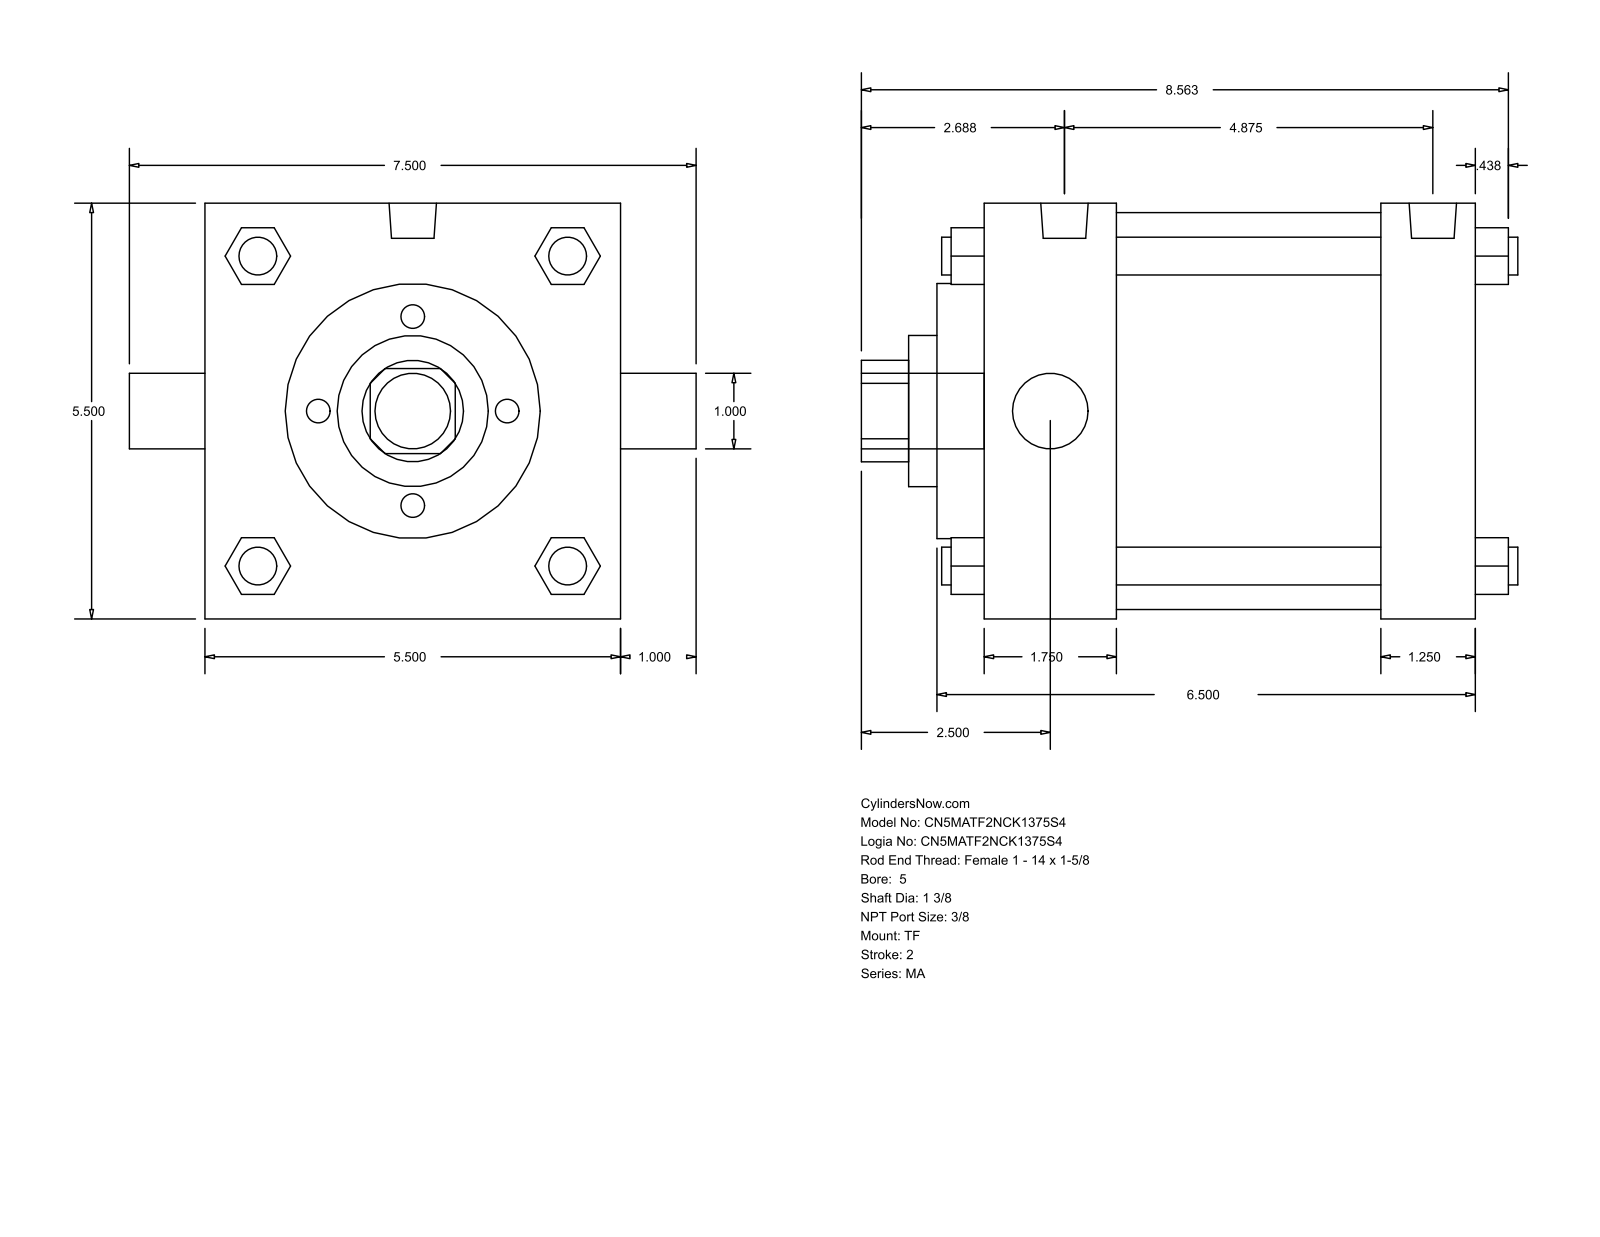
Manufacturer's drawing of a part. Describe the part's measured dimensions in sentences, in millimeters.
The part is named "MA_TF__0500_1.375". Its 3-D file was written by "GSSL Pune (CONFIG_CONTROL_DESIGN)". It is 0 solids with 122 faces: 93 planar, 29 cylindrical and 0 other. Overall it measures 220.66 by 190.5 by 139.7 millimeters. Round holes: 1 of diameter 25.4, 1 of diameter 34.92, 1 of diameter 50.8, 1 of diameter 85.72, 1 of diameter 133.35. Round bosses or shafts: 4 of diameter 12.7, 3 of diameter 11.11, 2 of diameter 15.93, 1 of diameter 25.4. Partial cylindrical surfaces (rounded edges, fillets, slot ends): 1 of radius 17.06. The main face-to-face distances are 139.7, 165.11, 133.35, 31.76, 44.45, 88.9, 120.66, 15.87, 60.32, 149.22.
